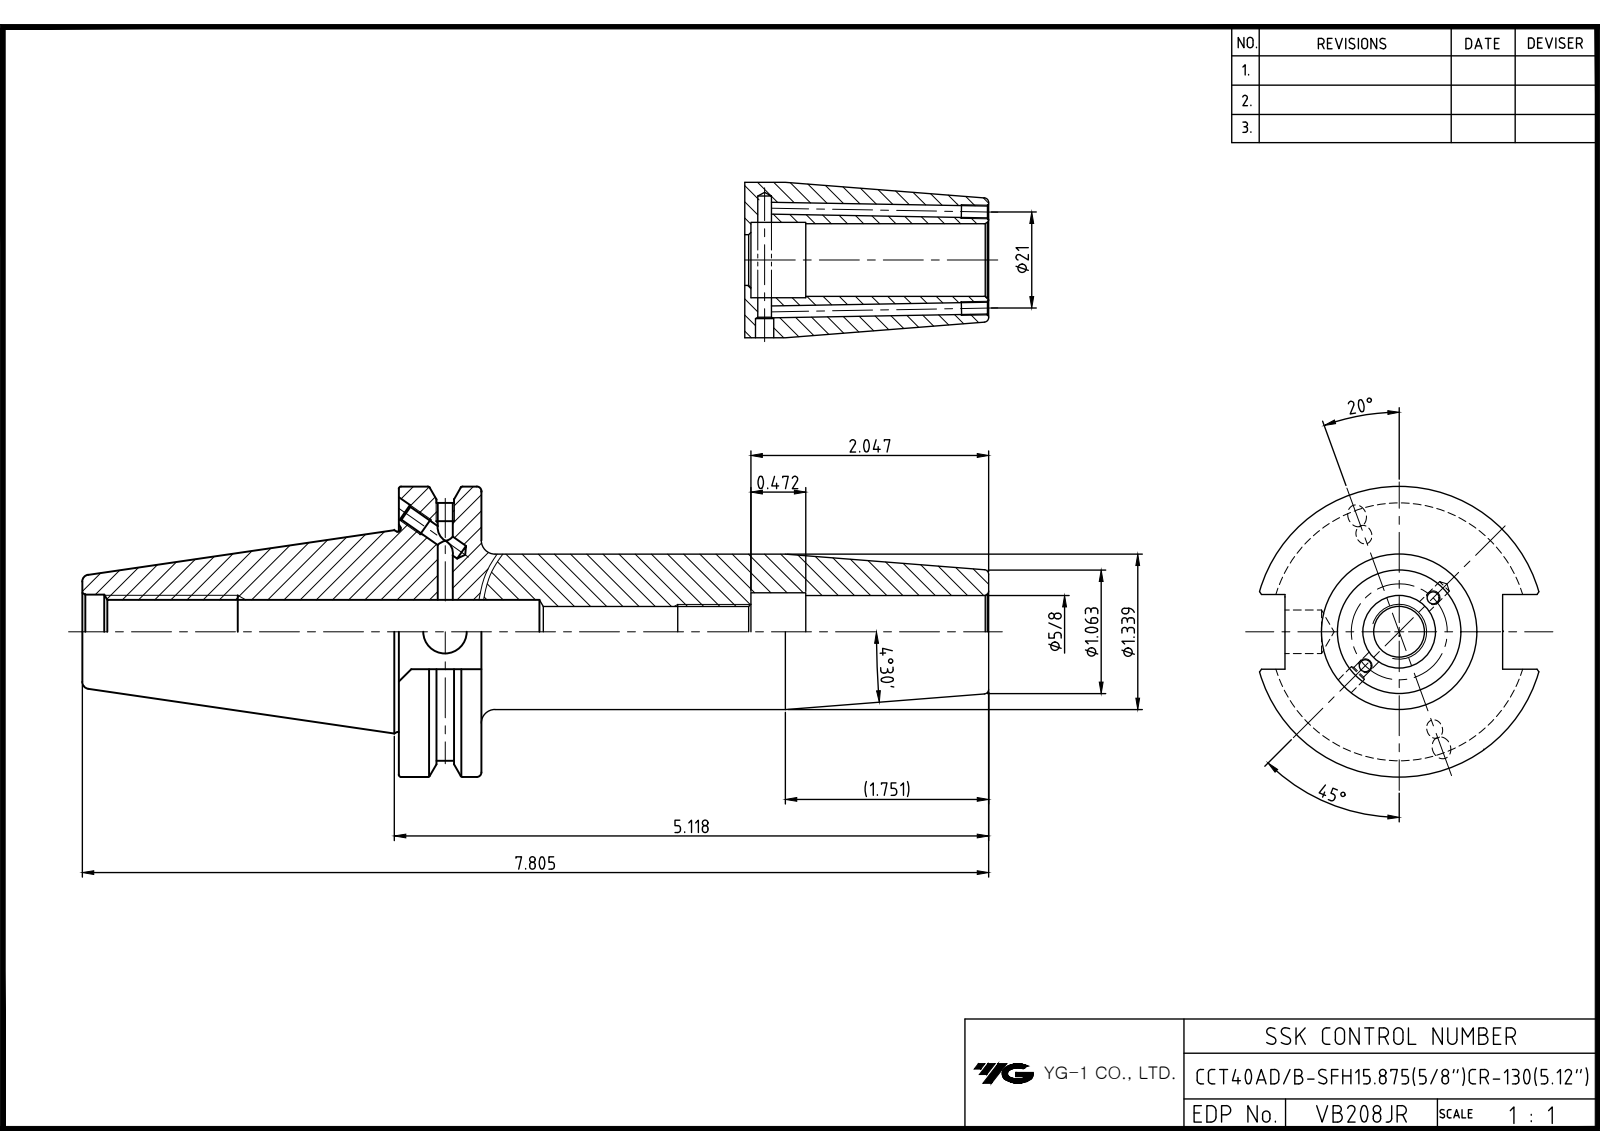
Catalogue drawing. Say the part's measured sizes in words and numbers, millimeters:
The part is named "LO-CCT40ADB-SFH15.875CR-130". Its 3-D file was written by "Autodesk Inventor 2026 (AUTOMOTIVE_DESIGN)". It is 1 solid with 88 faces: 37 planar, 29 cylindrical and 22 other. Overall it measures 198.25 by 63.5 by 61.09 millimeters. Its volume is 179 462 cubic millimeters and its surface area 37 385 square millimeters. Round holes: 4 of diameter 3.24, 2 of diameter 2.46, 2 of diameter 4, 2 of diameter 4.2, 1 of diameter 9.53, 1 of diameter 10.92, 1 of diameter 13.39, 1 of diameter 15.88, 1 of diameter 16.3, 1 of diameter 17. Round bosses or shafts: 1 of diameter 63.5, 1 of diameter 34. Partial cylindrical surfaces (rounded edges, fillets, slot ends): 1 of radius 28.15. The main face-to-face distances are 18.05, 129, 110.95, 47.6, 16.38, 69.25, 87.3, 198.25, 146.25, 77.
